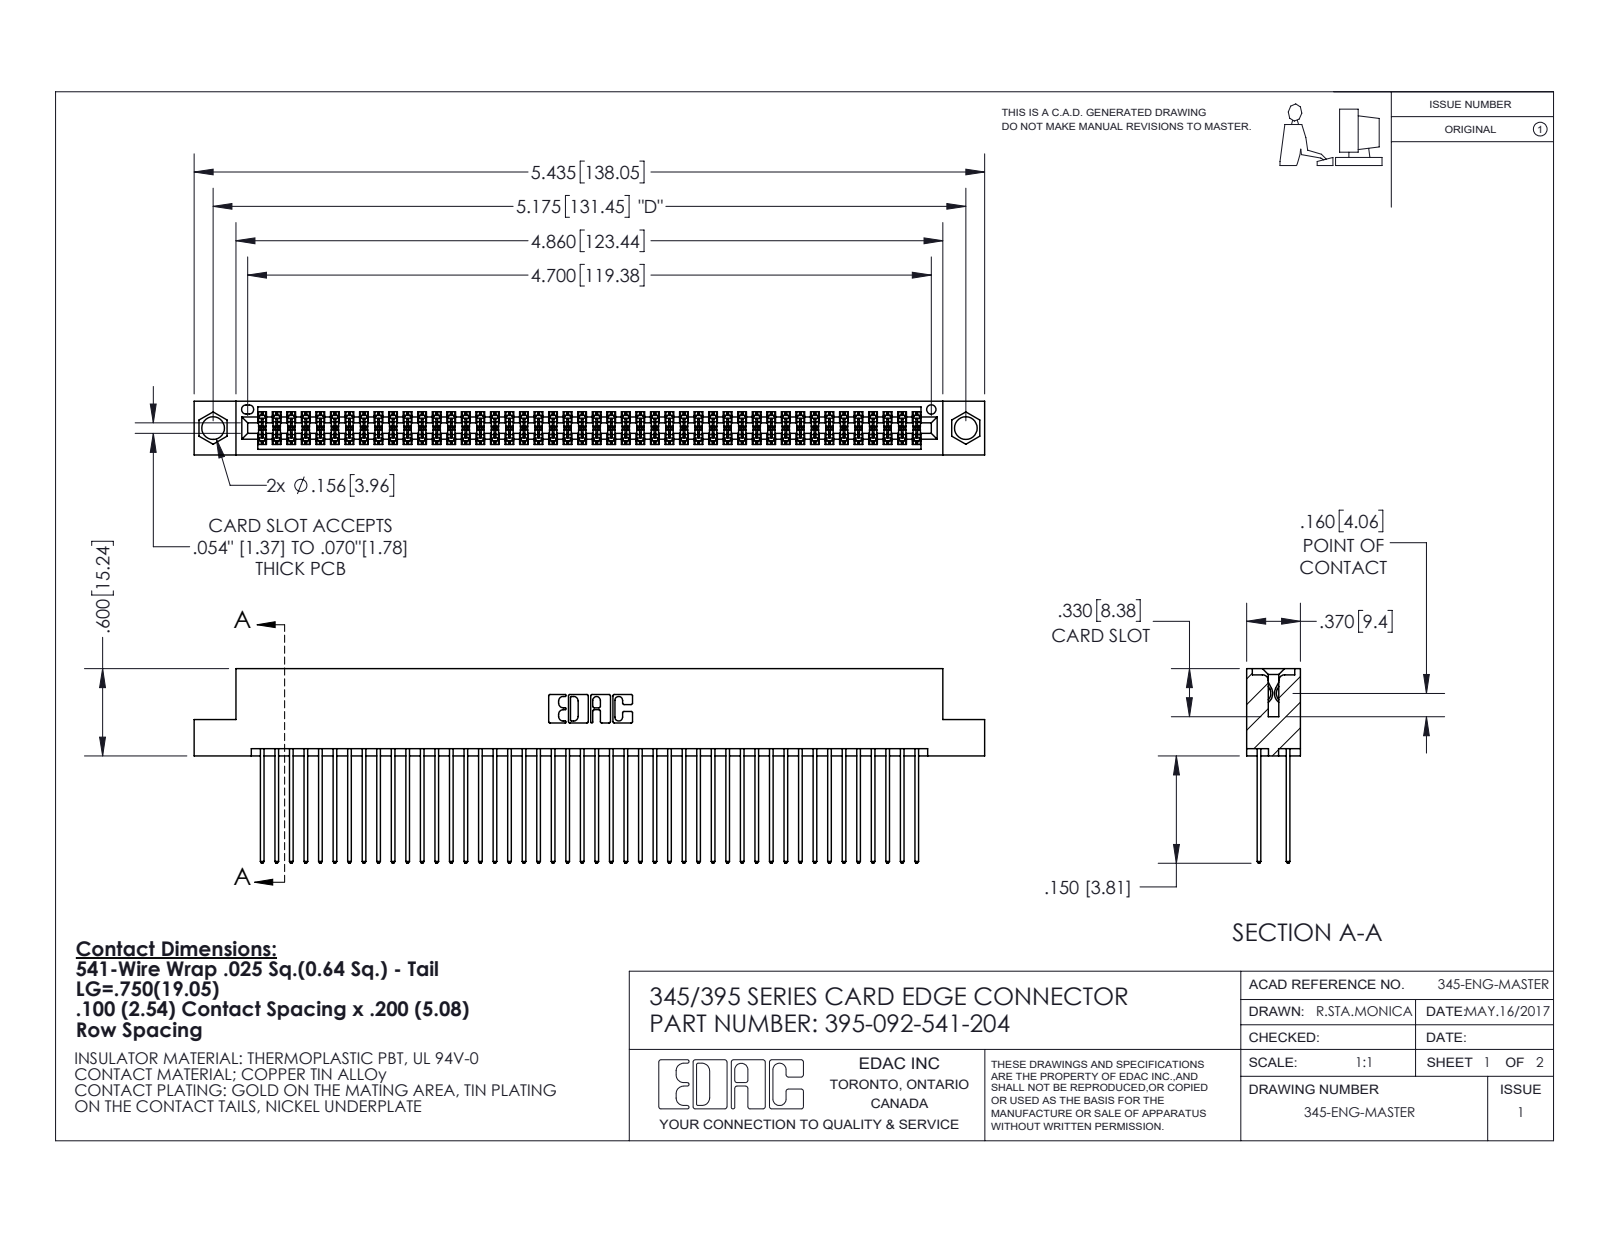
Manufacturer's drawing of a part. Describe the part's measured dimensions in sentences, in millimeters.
The part is named "345-292-001_345-293-141; 345 Part_Flush Mounting Lugs - 0.156 Dia-TI; 395-092-541-204". Its 3-D file was written by "SolidWorks 2020 (CONFIG_CONTROL_DESIGN)". It is 93 solids with 4740 faces: 3130 planar, 1610 cylindrical and 0 other. Overall it measures 138 by 34 by 9.4 millimeters. Its volume is 13 900 cubic millimeters and its surface area 22 910 square millimeters. Round holes: 2 of diameter 4, 1 of diameter 1.6. Partial cylindrical surfaces (rounded edges, fillets, slot ends): 183 of radius 0.2, 92 of radius 0.3, 22 of radius 0.3, 6 of radius 0.2, 6 of radius 0.8, 3 of radius 0.7, 2 of radius 0.4, 2 of radius 0.5. The main face-to-face distances are 1.8, 7.6, 5.1, 2.5, 6.9, 0.6, 5.7, 9.4, 4.4, 3.8. The hole center spacings are 6.9, 125.5, 131.4.
